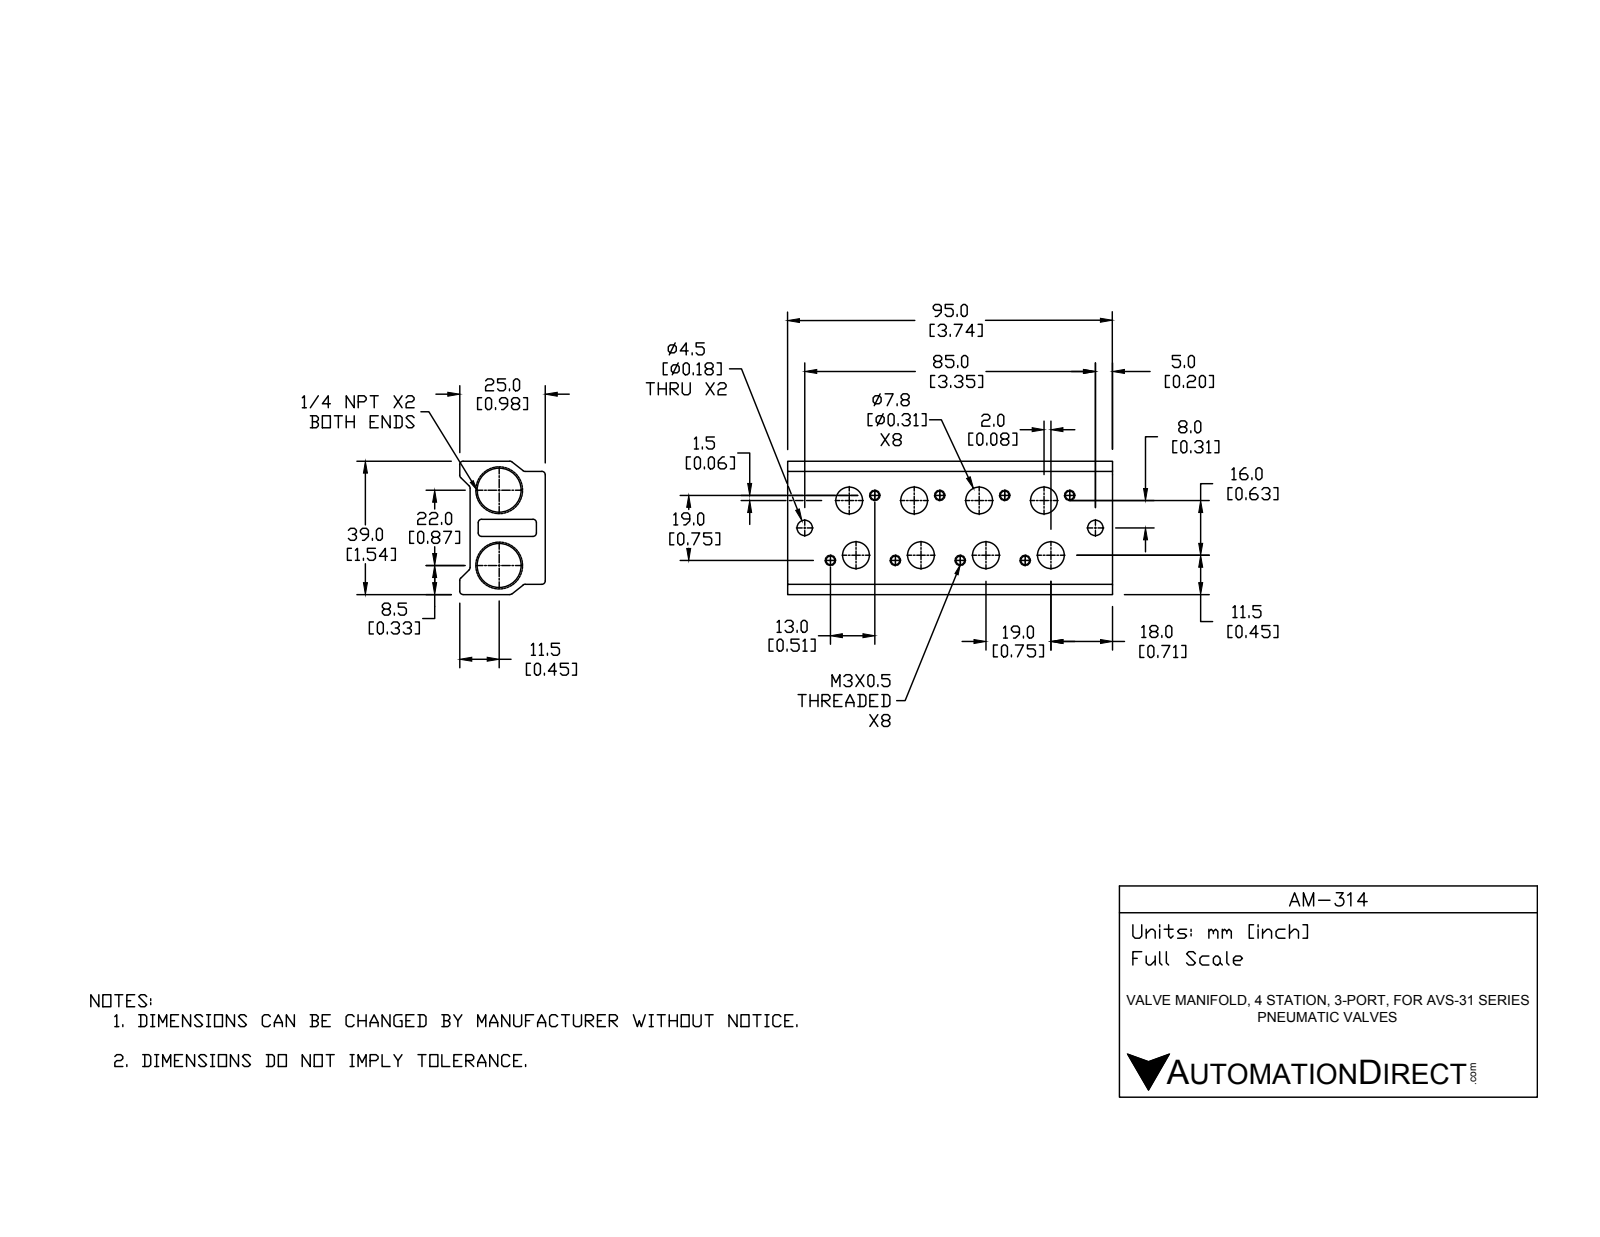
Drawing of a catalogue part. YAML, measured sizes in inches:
part_name: "AM-314"
step_written_by: "SolidWorks 2016 (AUTOMOTIVE_DESIGN)"
units: inches
bodies: {solids: 1, faces: 154, planar: 26, cylindrical: 78, other: 50}
overall_size: [3.74, 1.535, 0.984]
volume: 2.931
surface_area: 39.37
round_holes:
  - {diameter: 0.098, count: 8}
  - {diameter: 0.307, count: 8}
  - {diameter: 0.177, count: 2}
  - {diameter: 0.437, count: 2}
  - {diameter: 0.438, count: 2}
partial_cylinders:
  - {radius: 0.039, count: 16}
face_to_face_distances: [0.866, 0.669, 0.118, 0.197, 1.535, 1.417, 0.551, 0.748, 0.984, 3.74]
hole_center_spacings: [0.748, 0.301, 0.722, 1.496, 0.457, 0.87, 1.045, 1.185]
